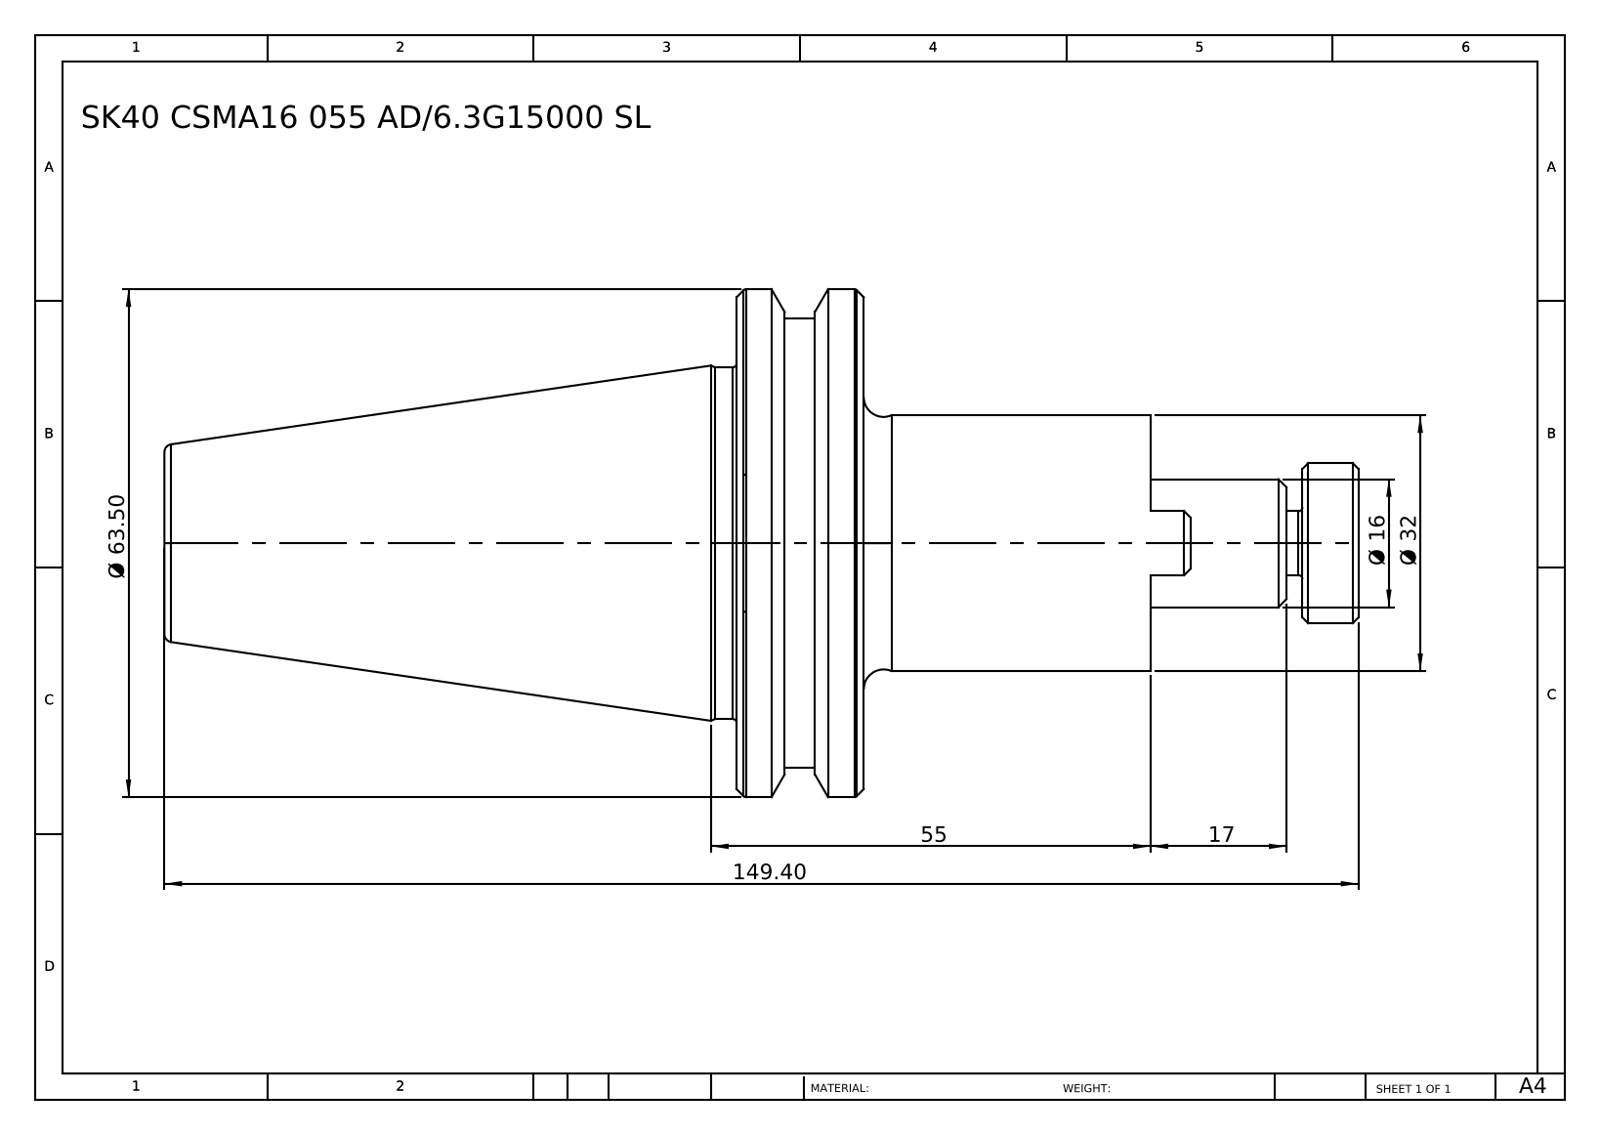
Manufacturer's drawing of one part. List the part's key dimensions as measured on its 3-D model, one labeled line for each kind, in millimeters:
Part name (STEP PRODUCT): SK 40 CSMA16 055 AD-6.3G15000 SL SP
STEP written by: SolidWorks 2014 (CONFIG_CONTROL_DESIGN)
Units: millimetres
Bodies: 1 solid, 82 faces (19 planar, 19 cylindrical, 44 other)
Overall size (bounding box): 149.4 × 63.55 × 63.55
Volume: 152 283 mm³ · Surface area: 22 473 mm²
Round holes (diameter × count): ⌀20 ×1
Round bosses / shafts (diameter × count): ⌀63.55 ×1, ⌀56.25 ×1, ⌀44 ×1, ⌀32 ×1, ⌀16 ×1, ⌀8 ×1
Main face-to-face distances: 15.9, 35.9, 51.8, 123.4, 87.5, 71.6, 26, 61.9, 77.8, 149.4
